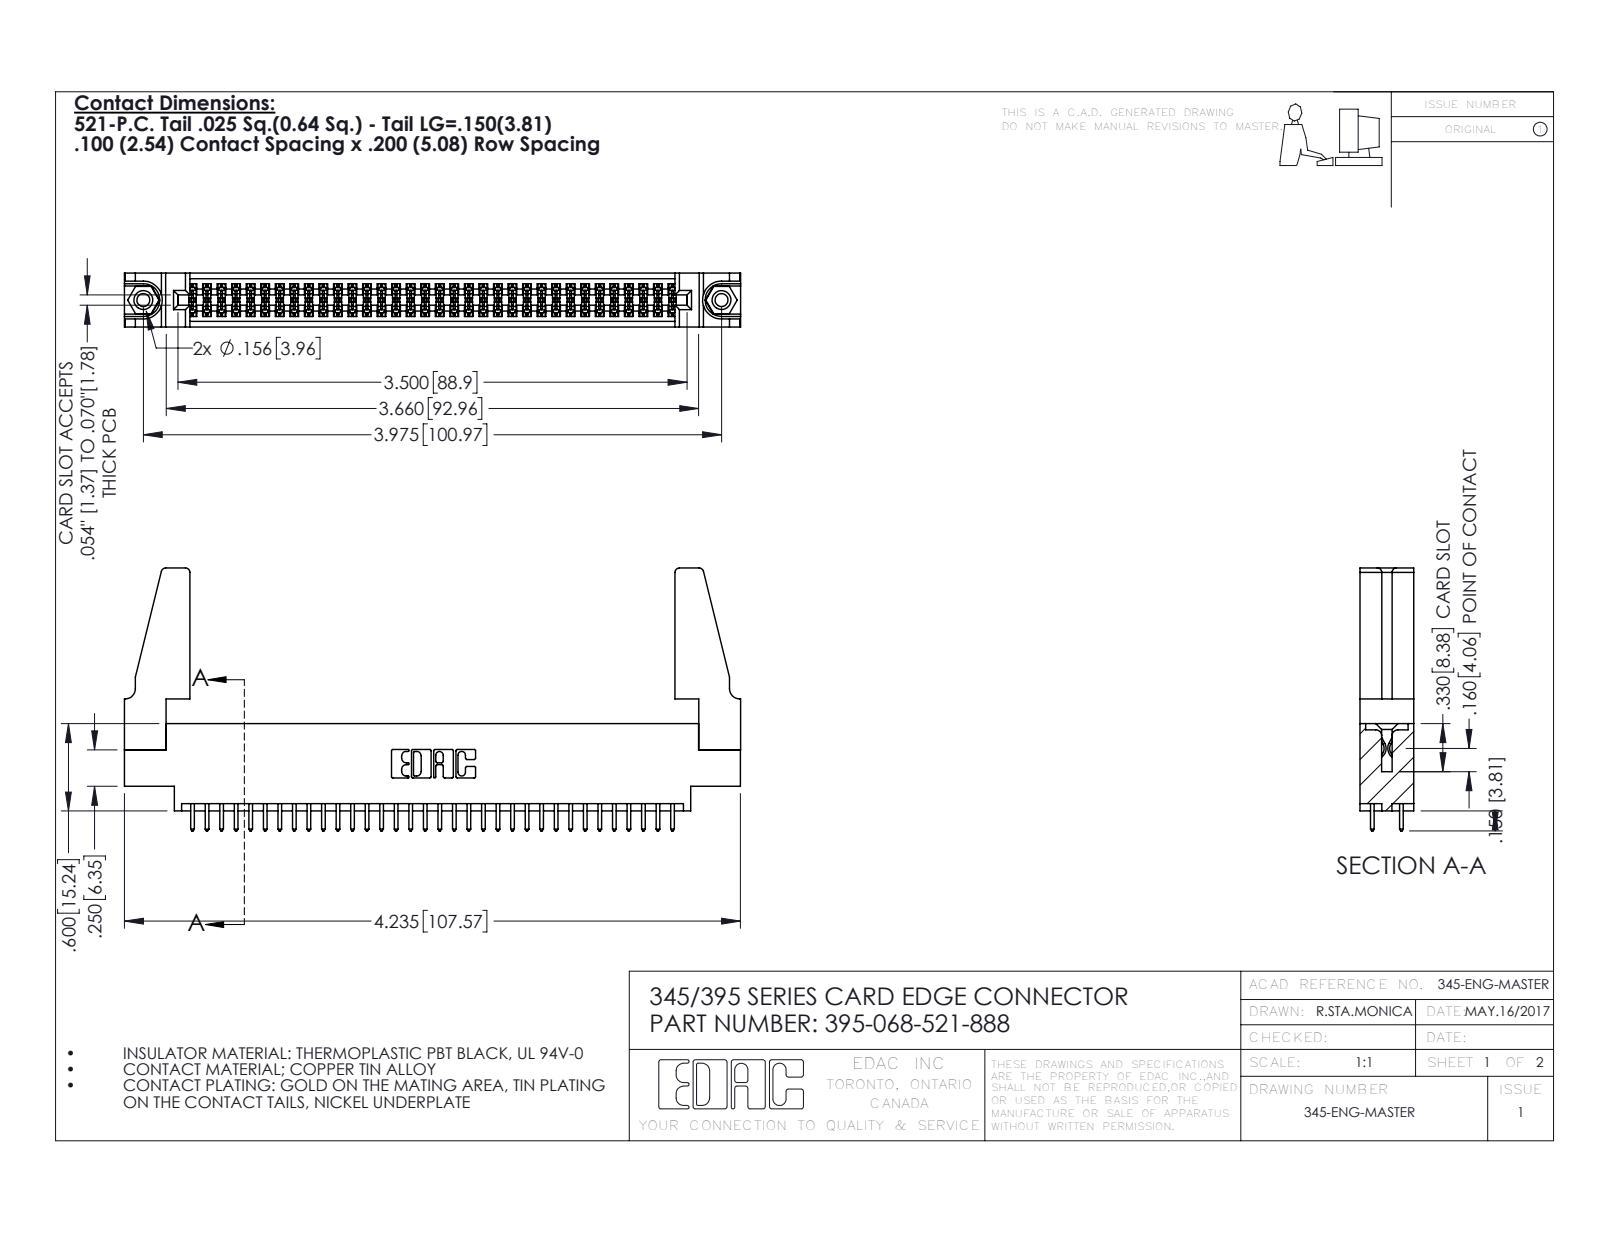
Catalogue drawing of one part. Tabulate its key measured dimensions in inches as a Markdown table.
| quantity | value |
| --- | --- |
| part name | 345 Part_0.170 Offset - 0.156 Dia-TH; 395-068-521-888; 345-250-001_345-250-001-102; 345-292-001_345-293-121 (+1 more) |
| STEP written by | SolidWorks 2016 (CONFIG_CONTROL_DESIGN) |
| units | inches |
| bodies | 73 solids, 3654 faces (2400 planar, 1238 cylindrical, 16 other) |
| overall size | 4.236 × 1.807 × 0.37 |
| volume | 0.823 in³ |
| surface area | 27.99 in² |
| round holes (diameter × count) | 0.089 × 2, 0.125 × 2, 0.156 × 2, 0.064 × 1 |
| round bosses / shafts (diameter × count) | 0.155 × 2 |
| partial cylindrical surfaces (radius × count) | 0.006 × 102, 0.01 × 68, 0.01 × 22, 0.03 × 8, 0.007 × 6, 0.031 × 6, 0.026 × 3, 0.014 × 2 |
| main face-to-face distances | 0.072, 0.298, 0.37, 0.2, 0.098, 0.272, 0.025, 0.225, 0.175, 0.149 |
| hole center spacings | 0.27, 3.74, 3.975 |
